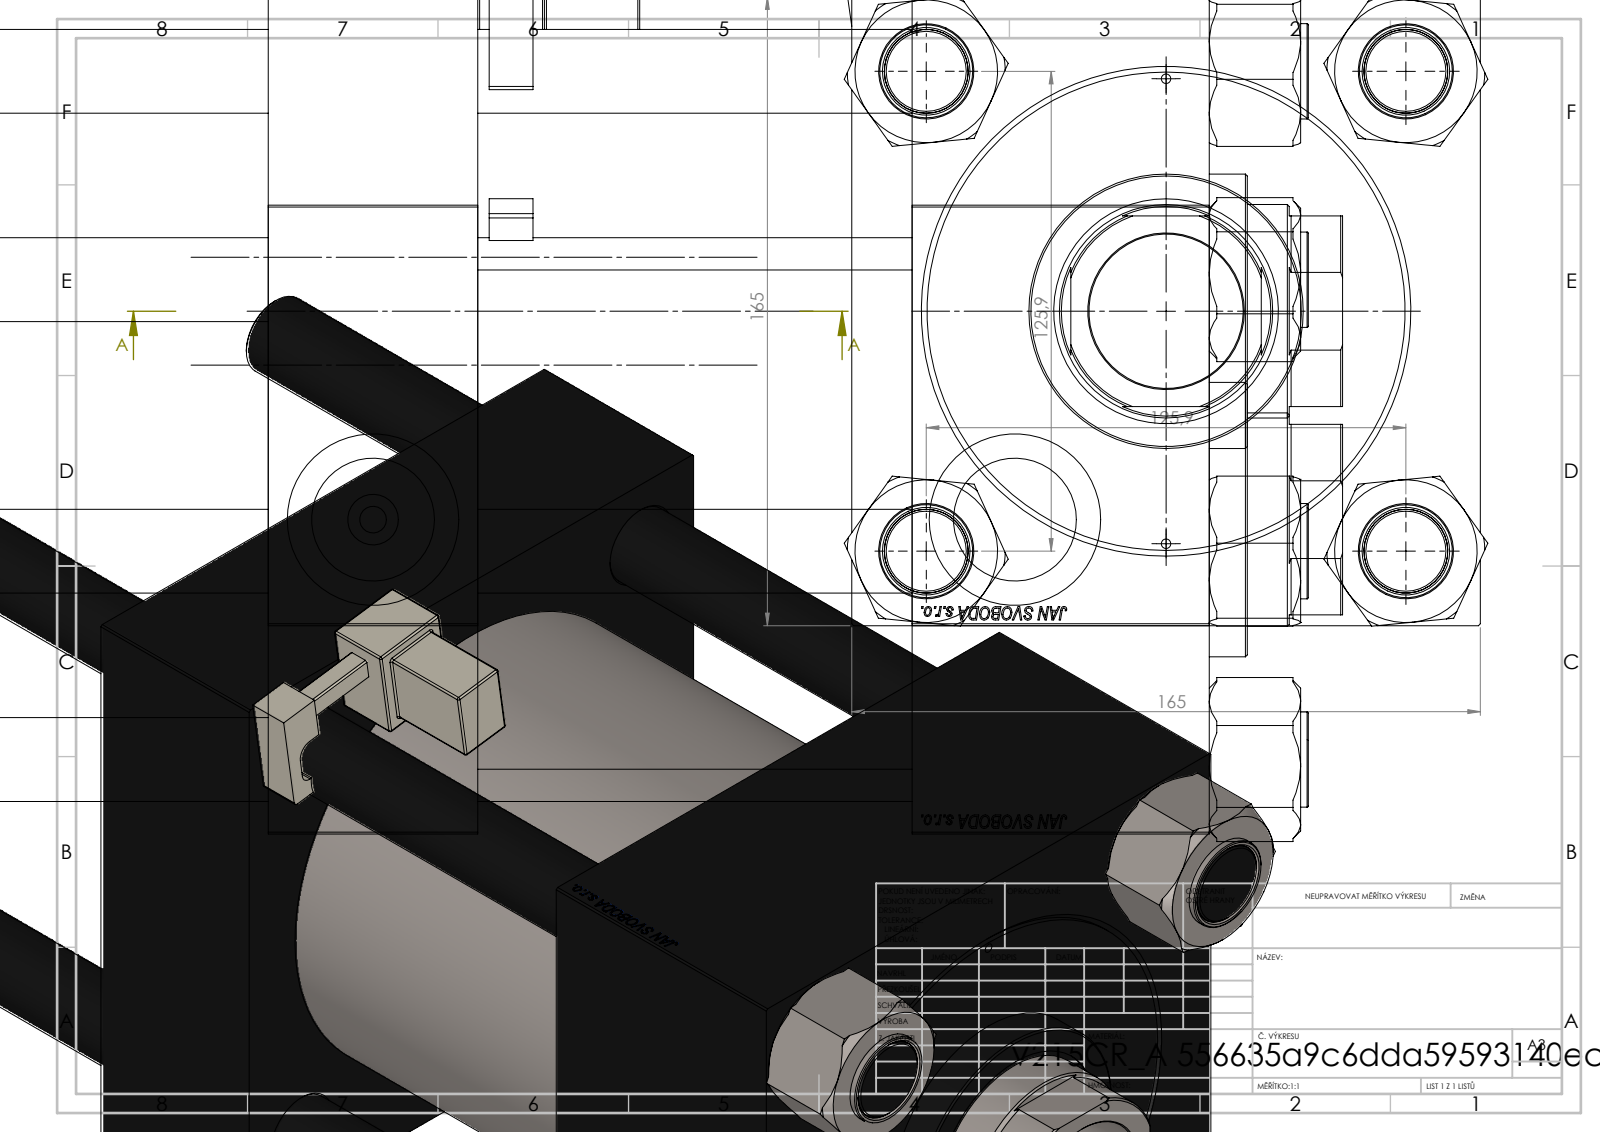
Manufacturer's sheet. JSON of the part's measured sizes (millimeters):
{"part_name": "V215CR_BODY_A; V215CR_VCP; NUT_M5; V215CR_MSU (+2 more)", "step_written_by": "SolidWorks 2019 (CONFIG_CONTROL_DESIGN)", "units": "millimeters", "bodies": {"solids": 12, "faces": 1265, "planar": 599, "cylindrical": 112, "other": 554}, "overall_size": [363, 178.03, 168.94], "volume_mm3": 4857000, "surface_area_mm2": 592789, "round_holes": [[22, 4], [2.5, 2], [7, 2], [32.24, 2], [45, 2], [40.5, 1], [56, 1], [59, 1], [96, 1], [125, 1], [125.5, 1]], "round_bosses_or_shafts": [[25, 4], [131, 1], [72, 1], [6, 1]], "partial_cylinders_radius": [[0.5, 24], [1, 1], [2.5, 1], [4, 1], [27, 1]], "face_to_face_distances": [165, 55, 247, 192, 114, 169, 78, 163.3, 218.3, 49.3], "hole_center_spacings": [62.98, 89.02, 125.9, 139.02, 61, 178.05, 122, 168.5]}
